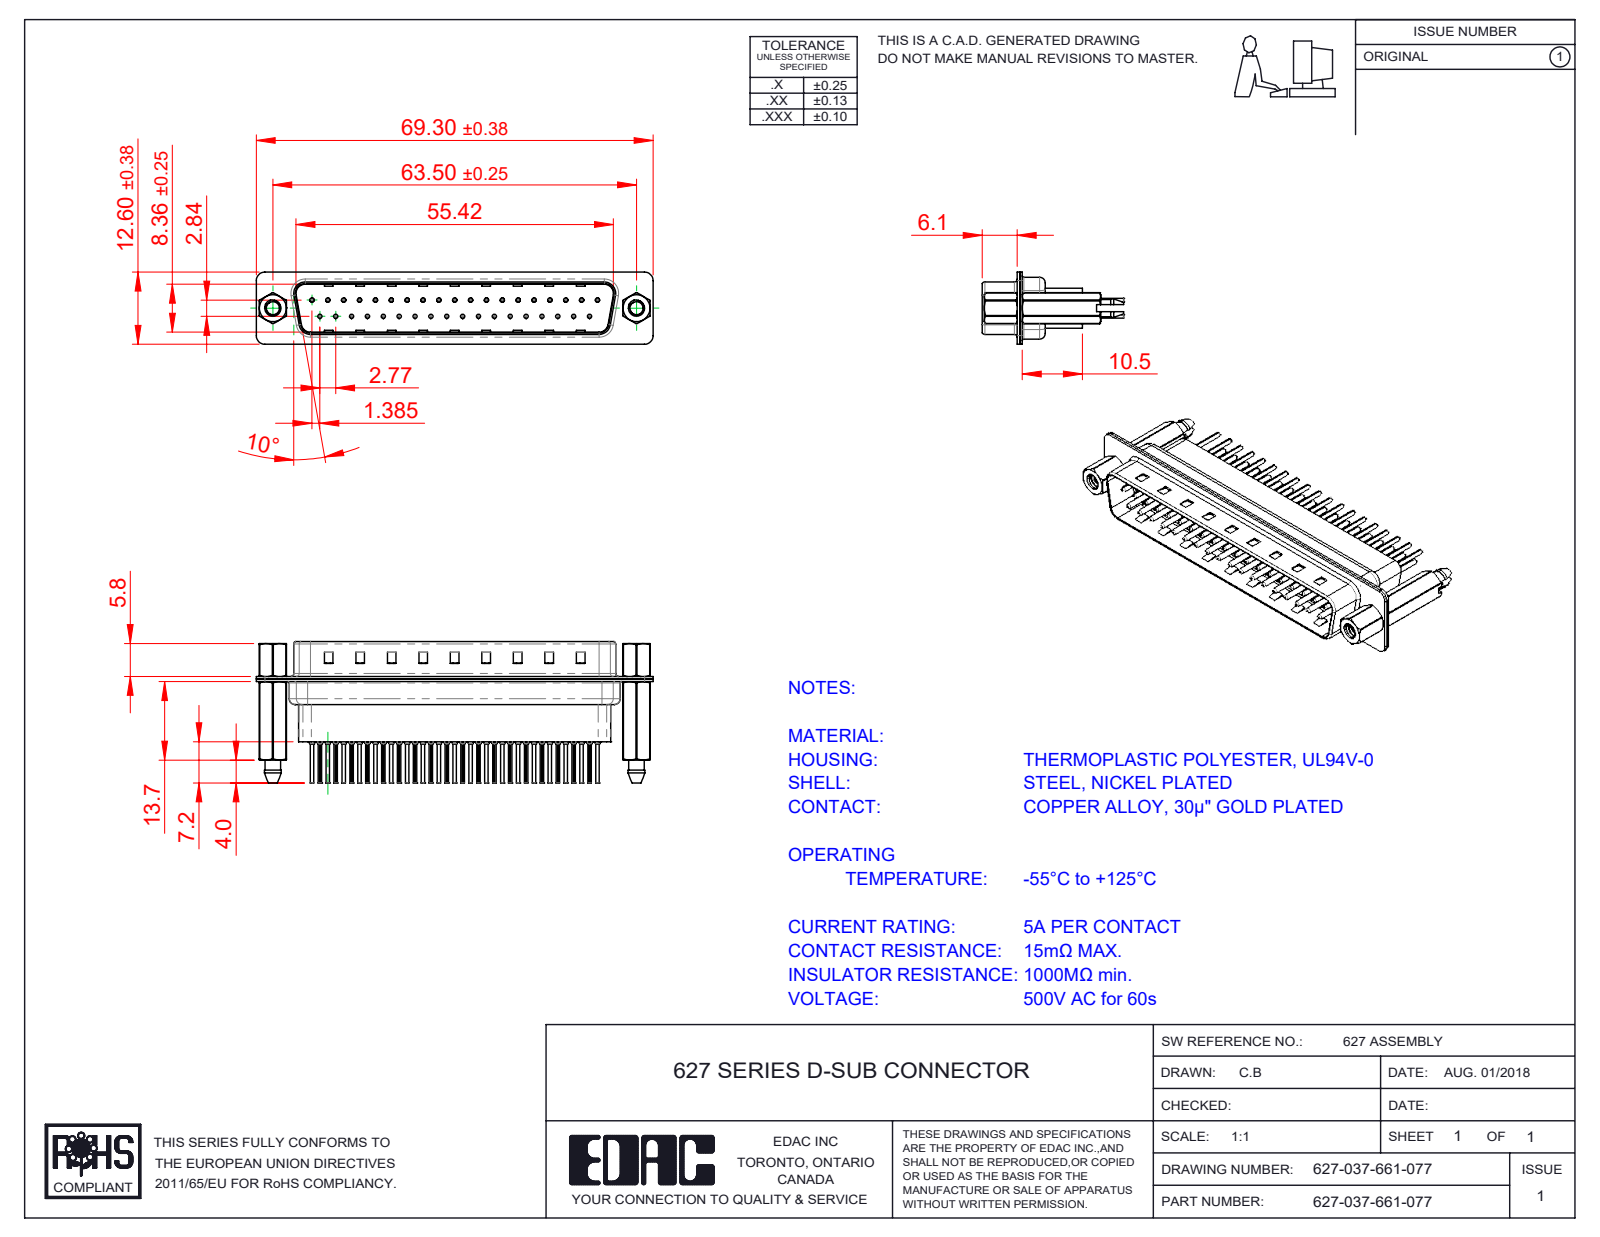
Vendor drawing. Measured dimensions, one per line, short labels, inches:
name: 627-037-661-077; 627 4-40 Threaded Boardlock_HP61; 627 Contact Row 2_61; 627 Contact Row 1_61 (+4 more)
written by: SolidWorks 2020 (CONFIG_CONTROL_DESIGN)
unit: in
bodies: 44 solids, 4272 faces (1145 planar, 1648 cylindrical, 1479 other)
size: 2.728 × 0.969 × 0.496
volume: 0.36 in³; area: 23.51 in²
holes: 37× ⌀0.008, 37× ⌀0.014, 37× ⌀0.043, 37× ⌀0.063, 2× ⌀0.089, 2× ⌀0.09, 2× ⌀0.157, 2× ⌀0.189
bosses: 37× ⌀0.079, 37× ⌀0.059, 37× ⌀0.03, 37× ⌀0.024, 2× ⌀0.193, 2× ⌀0.11
rounds: 74× R0.004, 18× R0.059, 12× R0.079, 10× R0.063, 8× R0.02, 4× R0.01, 4× R0.024, 4× R0.026
face distances: 0.016, 0.032, 0.377, 0.018, 0.027, 0.302, 0.059, 0.043, 0.318, 0.345
hole spacings: 0.124, 0.109, 0.218, 0.327, 0.198, 0.398, 0.436, 0.503
